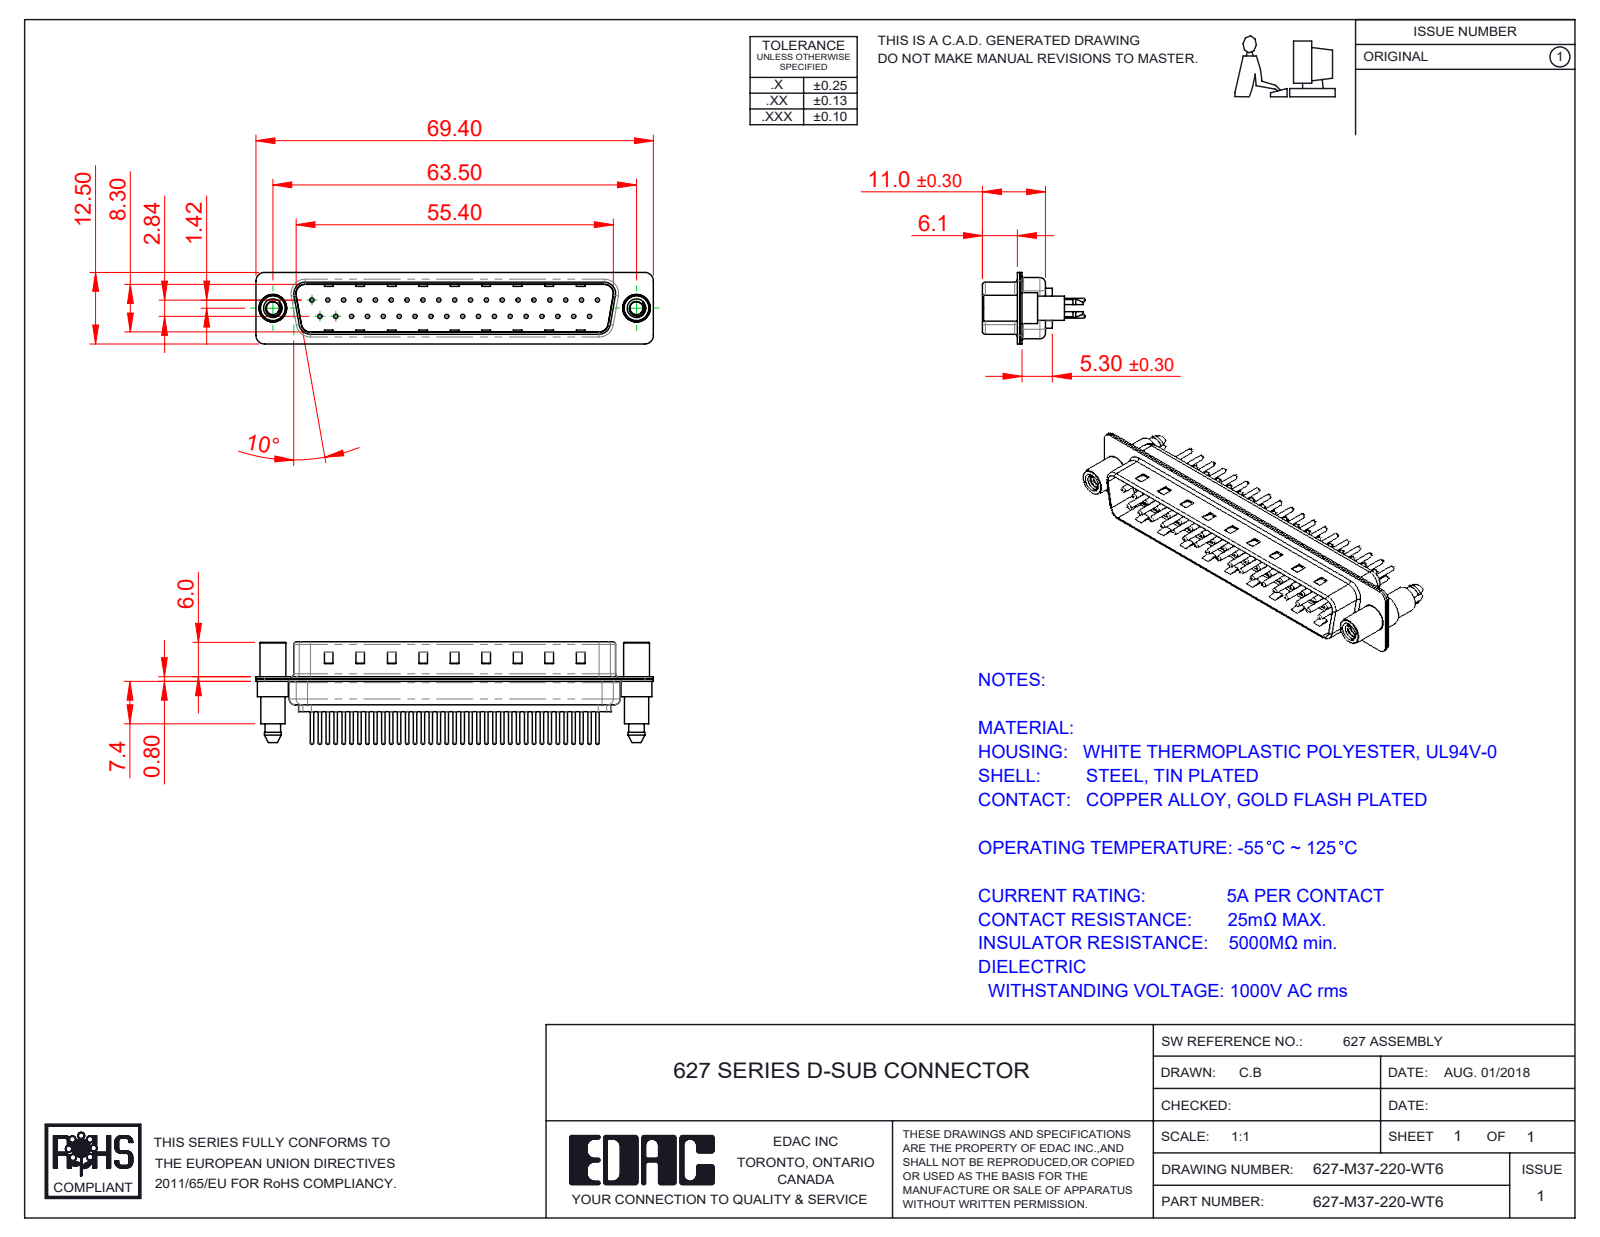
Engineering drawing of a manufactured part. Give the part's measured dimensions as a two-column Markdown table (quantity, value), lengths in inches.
| quantity | value |
| --- | --- |
| part name | 627M 4-40 Threaded Standoff and Boardlock; 627M Shell Rear_37 Contacts; 627M Shell Front_37 Contacts; 627M Contact Row 1_20 (+3 more) |
| STEP written by | SolidWorks 2020 (CONFIG_CONTROL_DESIGN) |
| units | inches |
| bodies | 42 solids, 1833 faces (480 planar, 687 cylindrical, 666 other) |
| overall size | 2.732 × 0.705 × 0.492 |
| volume | 0.251 in³ |
| surface area | 15.09 in² |
| round holes (diameter × count) | 0.03 × 37, 0.063 × 37, 0.079 × 37, 0.089 × 2, 0.157 × 2, 0.189 × 2 |
| round bosses / shafts (diameter × count) | 0.059 × 37, 0.024 × 37, 0.213 × 2, 0.193 × 2, 0.177 × 2, 0.167 × 2 |
| partial cylindrical surfaces (radius × count) | 0.059 × 18, 0.079 × 12, 0.063 × 10, 0.02 × 8, 0.01 × 4, 0.024 × 4, 0.026 × 4, 0.035 × 4 |
| main face-to-face distances | 0.016, 0.031, 0.374, 0.358, 0.343, 0.39, 0.047, 0.224, 0.03, 0.014 |
| hole center spacings | 0.109, 0.218, 0.124, 0.327, 0.436, 0.545, 0.654, 0.763 |
